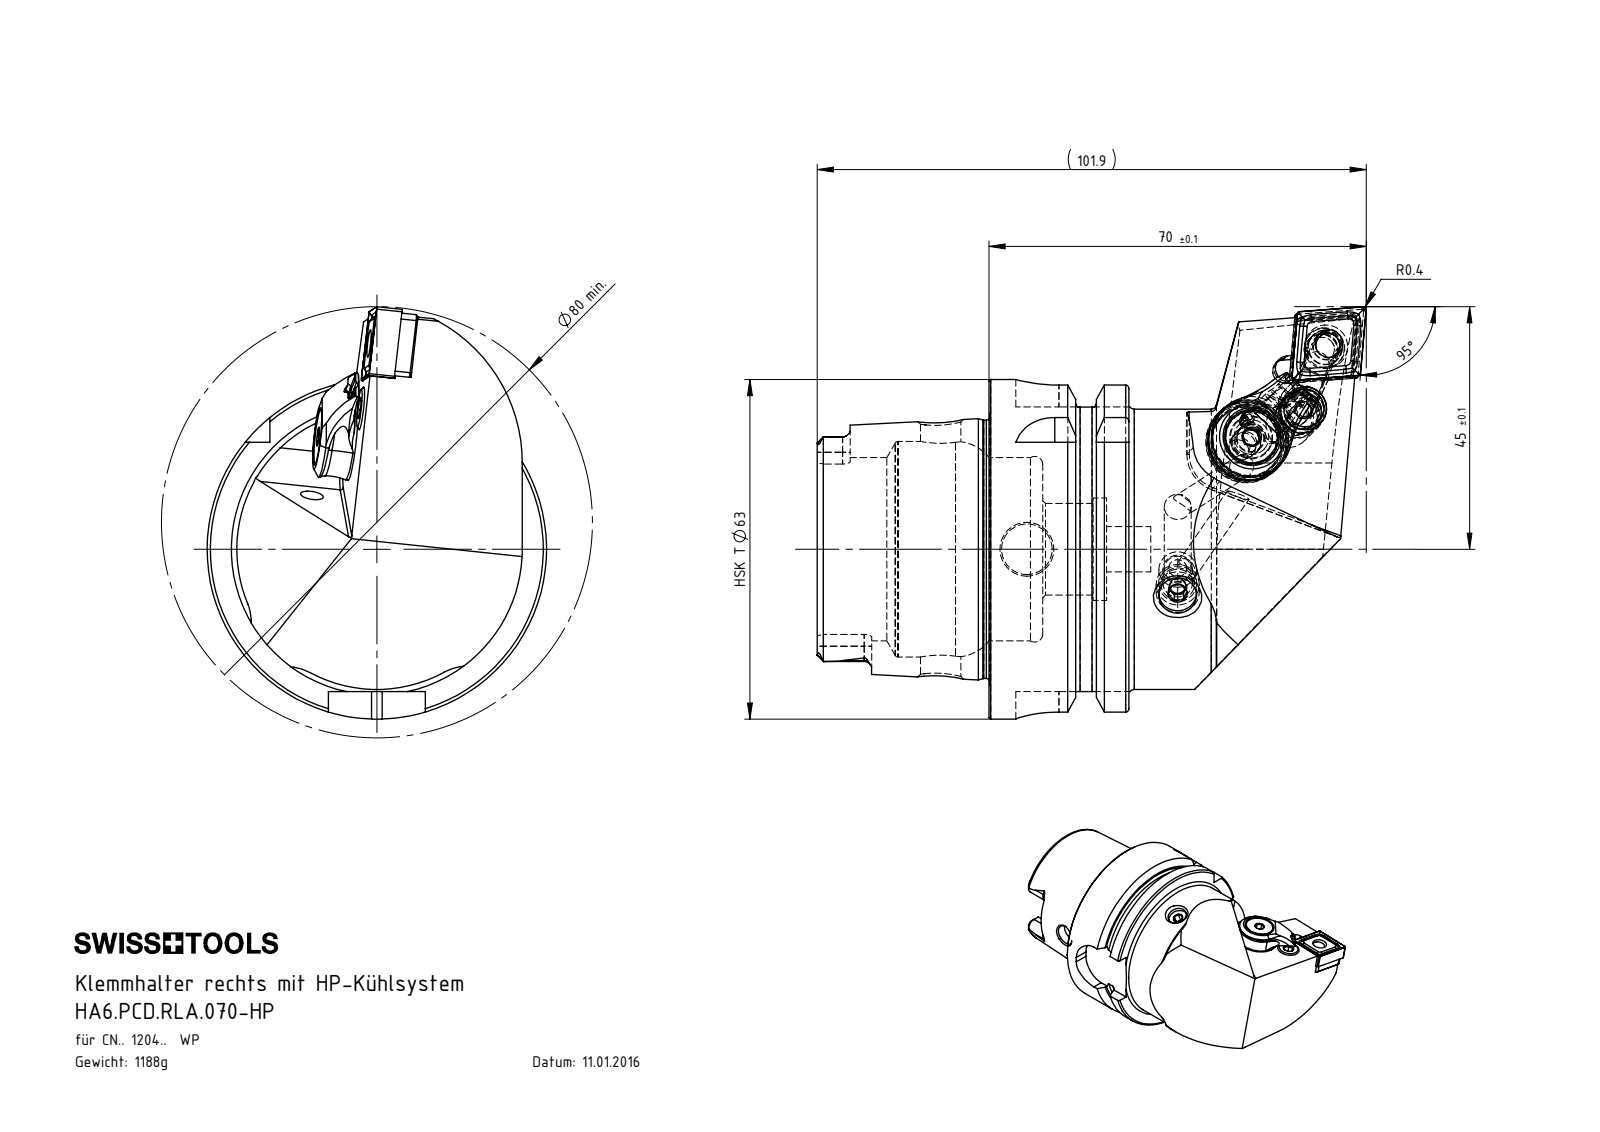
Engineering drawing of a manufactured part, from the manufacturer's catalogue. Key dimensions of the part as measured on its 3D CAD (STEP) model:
Part name (STEP PRODUCT): WCD-ER2.101.003_A; WCD-ER3.101.000_A; CHP-PCX.000.022_Dse; CHP-ER1.008.014_A (+8 more)
STEP written by: SolidWorks 2017 (AUTOMOTIVE_DESIGN)
Units: millimetres
Bodies: 11 solids, 584 faces (171 planar, 170 cylindrical, 243 other)
Overall size (bounding box): 101.9 × 76.5 × 63
Volume: 150 918 mm³ · Surface area: 36 204 mm²
Round holes (diameter × count): ⌀4.2 ×3, ⌀7 ×2, ⌀8.4 ×2, ⌀1.2 ×1, ⌀2 ×1, ⌀3 ×1, ⌀5 ×1, ⌀5.16 ×1, ⌀5.3 ×1, ⌀6.4 ×1, ⌀7.5 ×1, ⌀10 ×1
Round bosses / shafts (diameter × count): ⌀8 ×2, ⌀63 ×1, ⌀54.95 ×1, ⌀52 ×1, ⌀47.94 ×1, ⌀14.85 ×1, ⌀13.4 ×1, ⌀10 ×1
Partial cylindrical surfaces — rounded edges, fillets, slot ends (radius × count): R1 ×11, R1.4 ×6, R0.4 ×4, R0.5 ×4, R8 ×4, R6 ×3, R1.1 ×2, R1.2 ×2
Main face-to-face distances: 25.95, 16, 9.95, 31.9, 41.85, 57.85, 52.8, 21.8, 11.85, 4.46
Hole centre spacings: 4.51, 10.44, 20.03, 12.23, 12.79, 12.85, 20.08, 20.09
